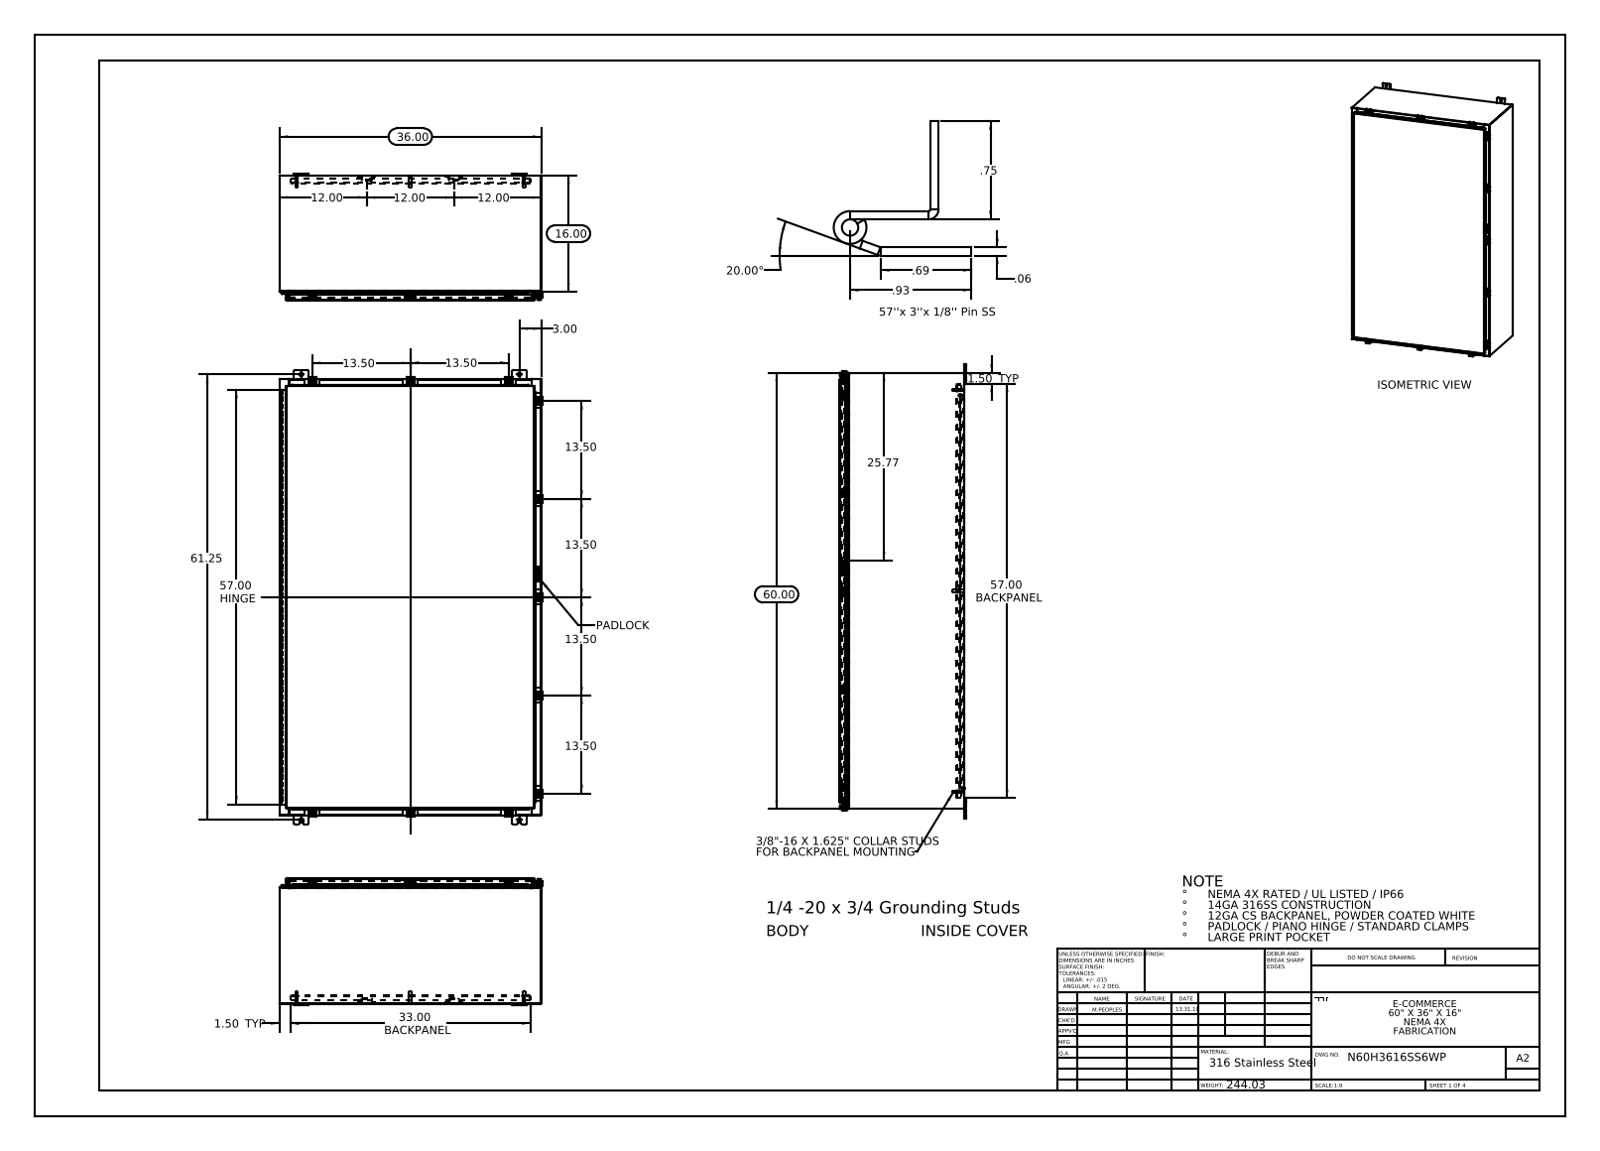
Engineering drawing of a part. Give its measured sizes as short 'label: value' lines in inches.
name: N60H3616SS6WP Mounting Studs; N60H3616SS6WP Clamp Top; N60H3616SS6WP Body; N60H3616SS6WP Hinge Cover Side (+8 more)
written by: SolidWorks 2013 (CONFIG_CONTROL_DESIGN)
unit: in
bodies: 79 solids, 3408 faces (1766 planar, 1466 cylindrical, 176 other)
size: 62.5 × 36.211 × 17.389
volume: 853.2 in³; area: 21 384 in²
holes: 12× ⌀0.5, 11× ⌀0.213, 11× ⌀0.26, 8× ⌀0.25, 2× ⌀0.125, 1× ⌀0.125
bosses: 12× ⌀0.25, 11× ⌀0.5, 11× ⌀0.399, 8× ⌀0.625, 8× ⌀0.375, 8× ⌀0.33
rounds: 50× R0.06, 39× R0.013, 33× R0.088, 24× R0.19, 22× R0.12, 22× R0.141, 17× R0.05, 16× R0.08
face distances: 0.075, 17.126, 17.051, 0.104, 17.201, 35.925, 16.126, 1, 1.075, 16.051
hole spacings: 13.5, 13.663, 2.225, 27, 27.625, 29.802, 41.709, 57.39
